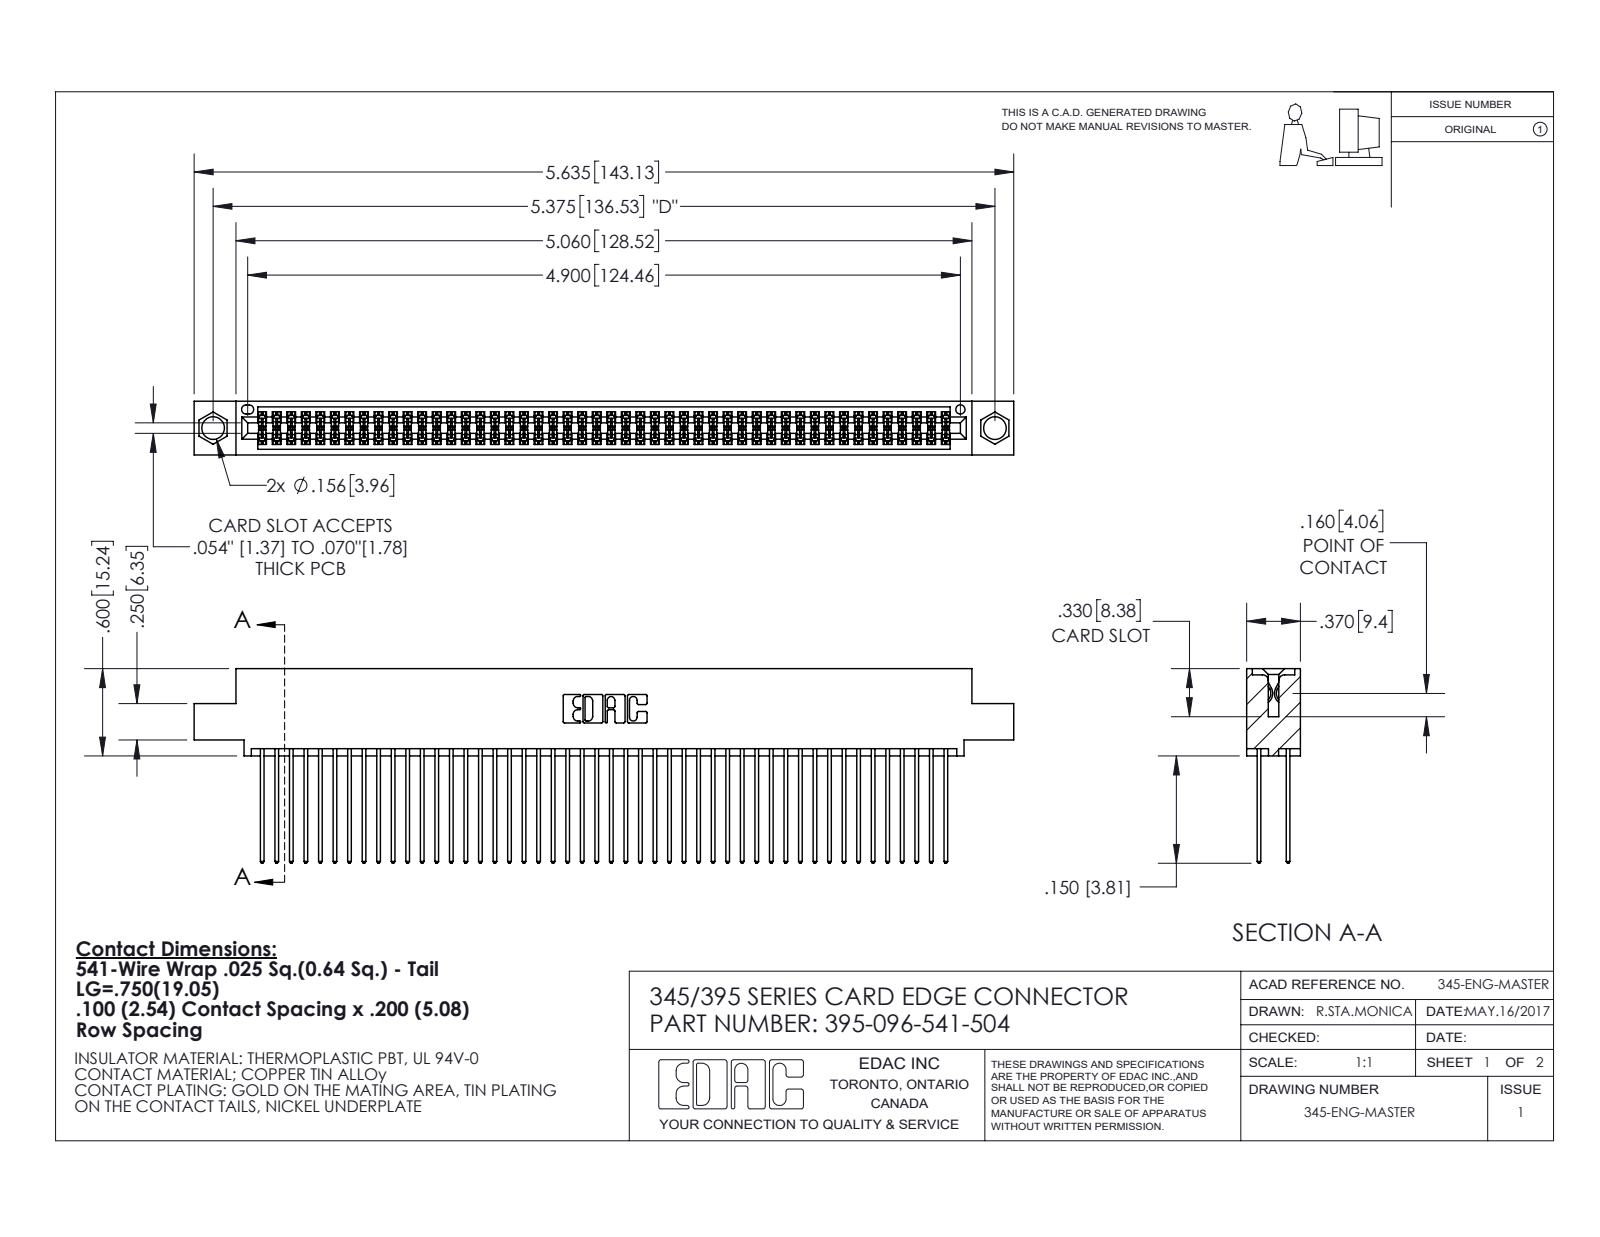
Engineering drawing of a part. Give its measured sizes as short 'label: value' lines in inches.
name: 345-292-001_345-293-141; 395-096-541-504; 345 Part_0.110 Offset - 0.156 Dia-TI
written by: SolidWorks 2020 (CONFIG_CONTROL_DESIGN)
unit: in
bodies: 97 solids, 4944 faces (3266 planar, 1678 cylindrical, 0 other)
size: 5.635 × 1.337 × 0.37
volume: 0.875 in³; area: 36.94 in²
holes: 2× ⌀0.156, 1× ⌀0.064
rounds: 144× R0.006, 96× R0.01, 22× R0.01, 6× R0.007, 6× R0.031, 3× R0.026, 2× R0.014, 2× R0.019
face distances: 0.298, 0.072, 0.2, 0.098, 0.272, 0.025, 0.225, 0.37, 0.175, 0.149
hole spacings: 0.27, 5.139, 5.375
